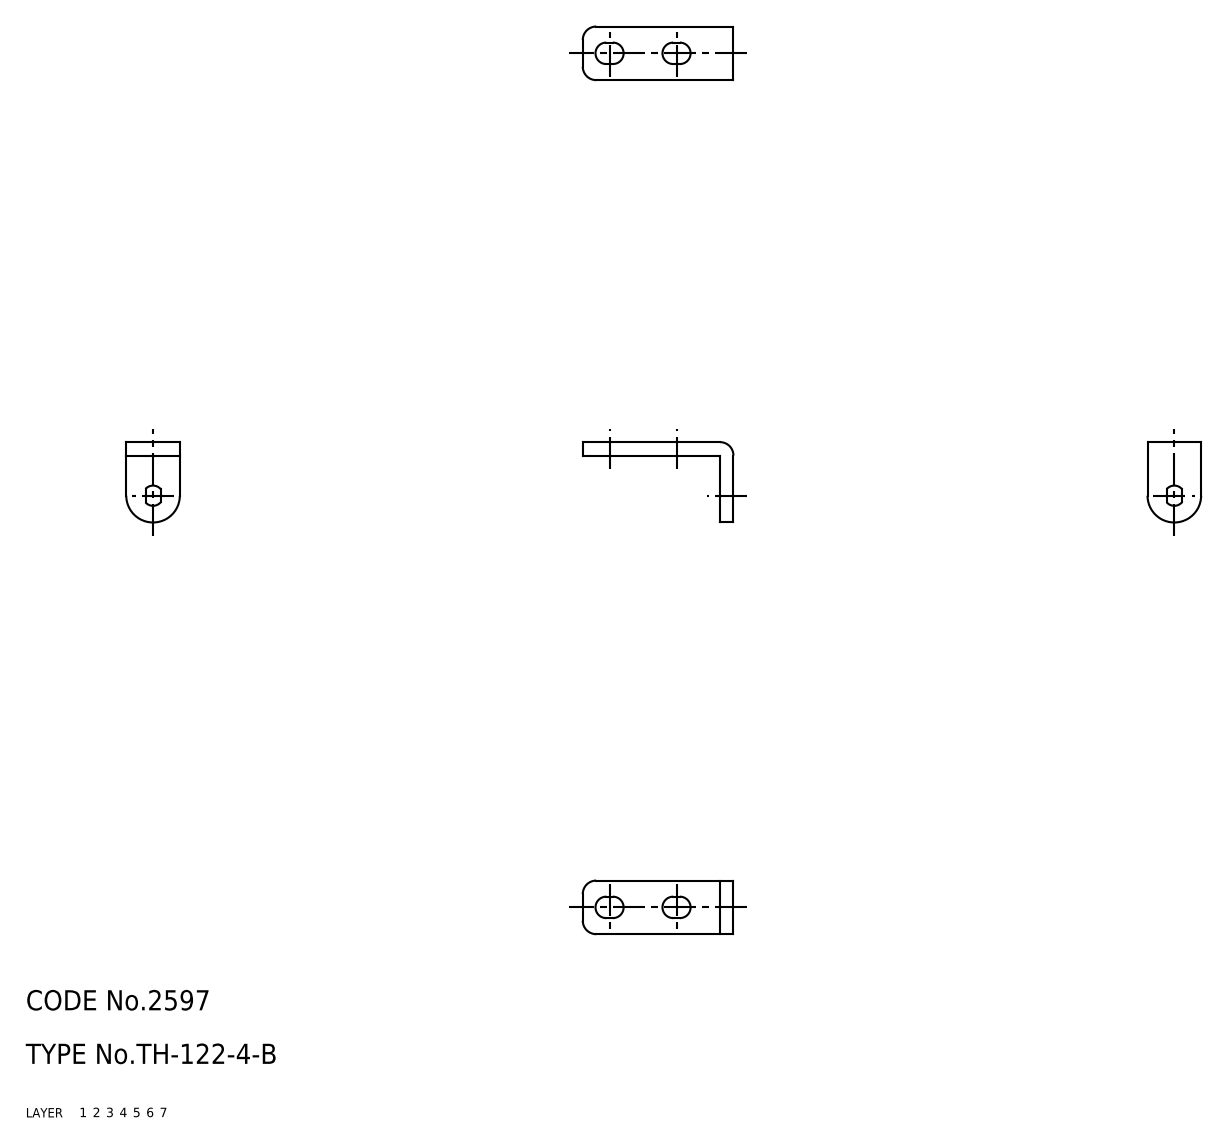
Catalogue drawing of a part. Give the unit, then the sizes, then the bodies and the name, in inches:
Units: inches
Overall size (bounding box): 0.886 × 0.472 × 0.315
Volume: 0.027 in³ · Surface area: 1.02 in²
Bodies: 1 solid, 23 faces (0 planar, 0 cylindrical, 23 other)
Part name (STEP PRODUCT): 67109942
STEP written by: CADfix (AUTOMOTIVE_DESIGN)
